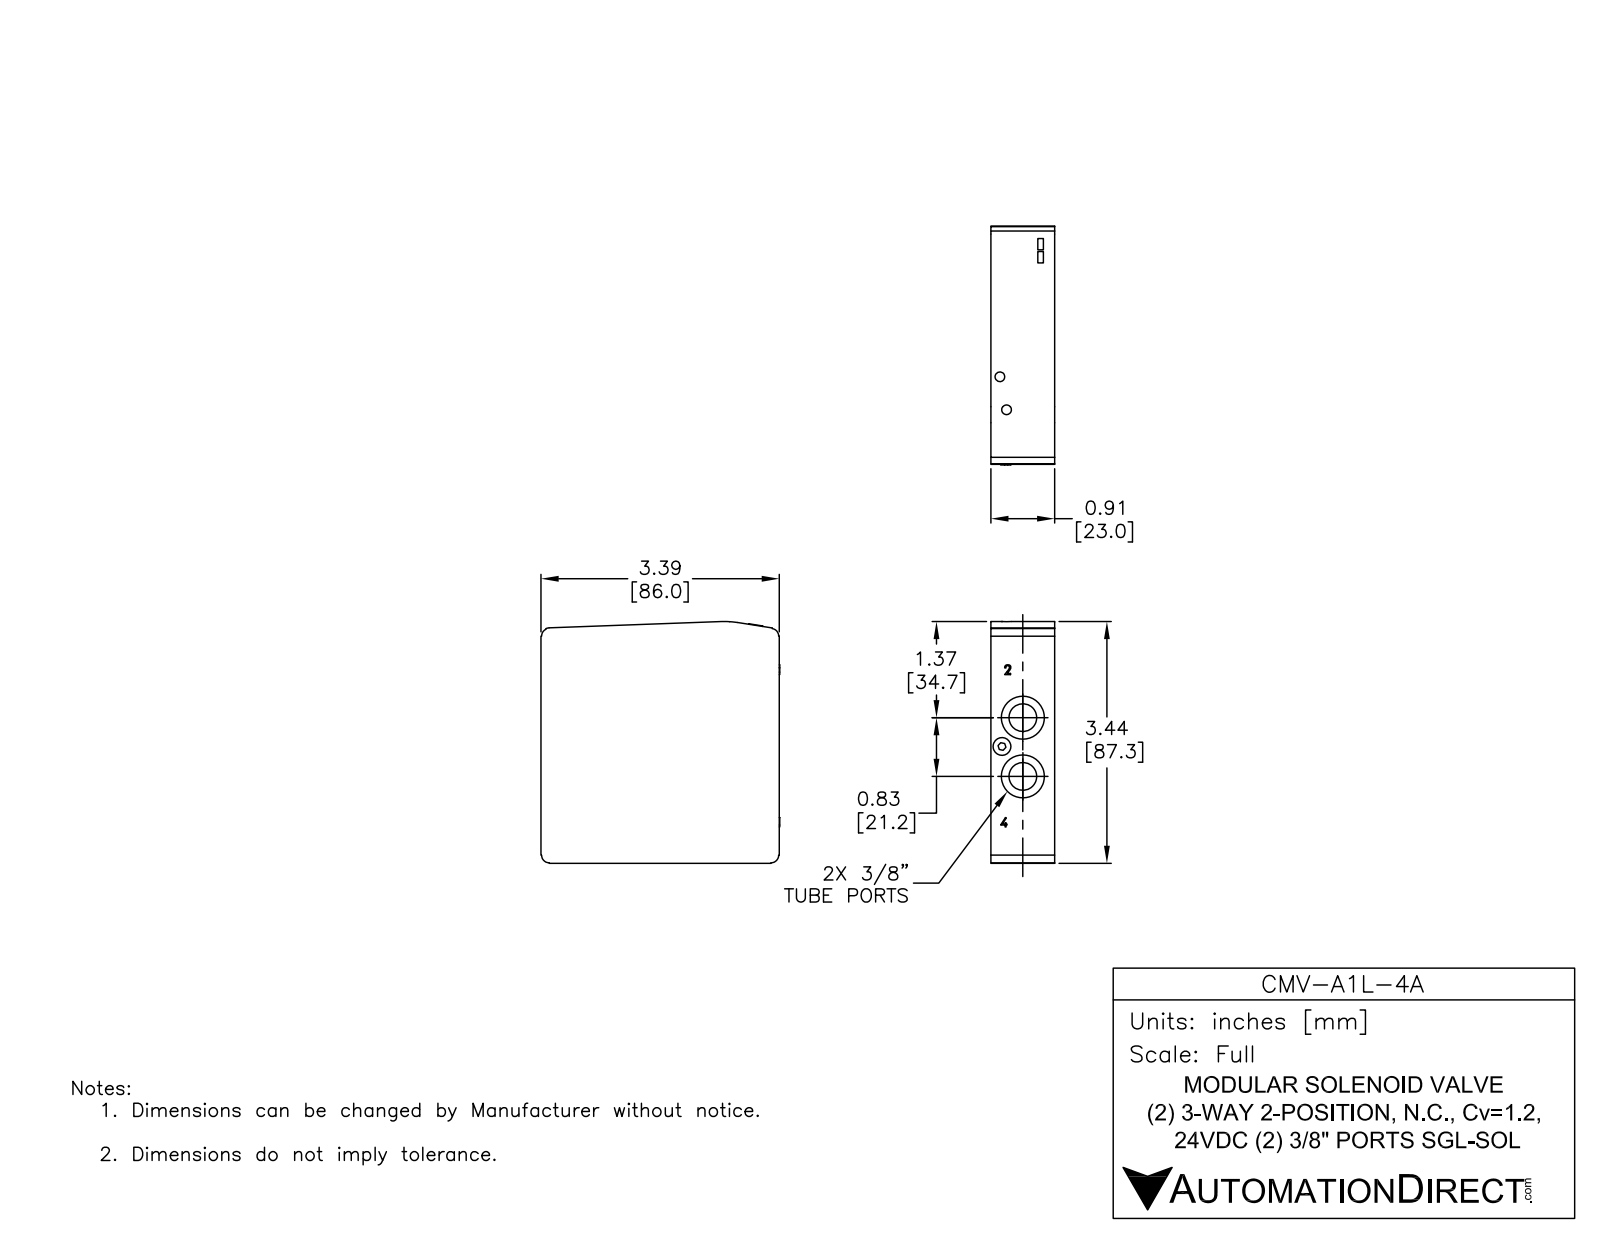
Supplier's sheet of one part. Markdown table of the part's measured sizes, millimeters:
| quantity | value |
| --- | --- |
| part name | CMV-A1L-4A |
| STEP written by | SolidWorks 2013 (AUTOMOTIVE_DESIGN) |
| units | millimeters |
| bodies | 75 solids, 1148 faces (899 planar, 162 cylindrical, 87 other) |
| overall size | 89.5 × 87.3 × 31.43 |
| volume | 154 040 mm³ |
| surface area | 54 384 mm² |
| round holes (diameter × count) | 4.4 × 4, 5.25 × 4, 3.35 × 2, 6.5 × 2, 9.75 × 2, 14 × 2, 18 × 2, 3.6 × 1, 6.25 × 1 |
| round bosses / shafts (diameter × count) | 4 × 4, 1.5 × 4, 15.25 × 2, 11 × 2, 6.25 × 2, 5.75 × 2, 4.2 × 2, 3.5 × 1 |
| partial cylindrical surfaces (radius × count) | 2.35 × 12, 0.78 × 4, 1.5 × 4, 2.8 × 4, 0.15 × 2, 0.25 × 2, 1 × 2, 2.25 × 2 |
| main face-to-face distances | 22.5, 12.5, 10, 83, 3, 1, 65.12, 50.25, 32.75, 53.25 |
| hole center spacings | 9.7, 11.99, 12.17, 16, 22.17, 31.45, 31.52, 39.5 |
